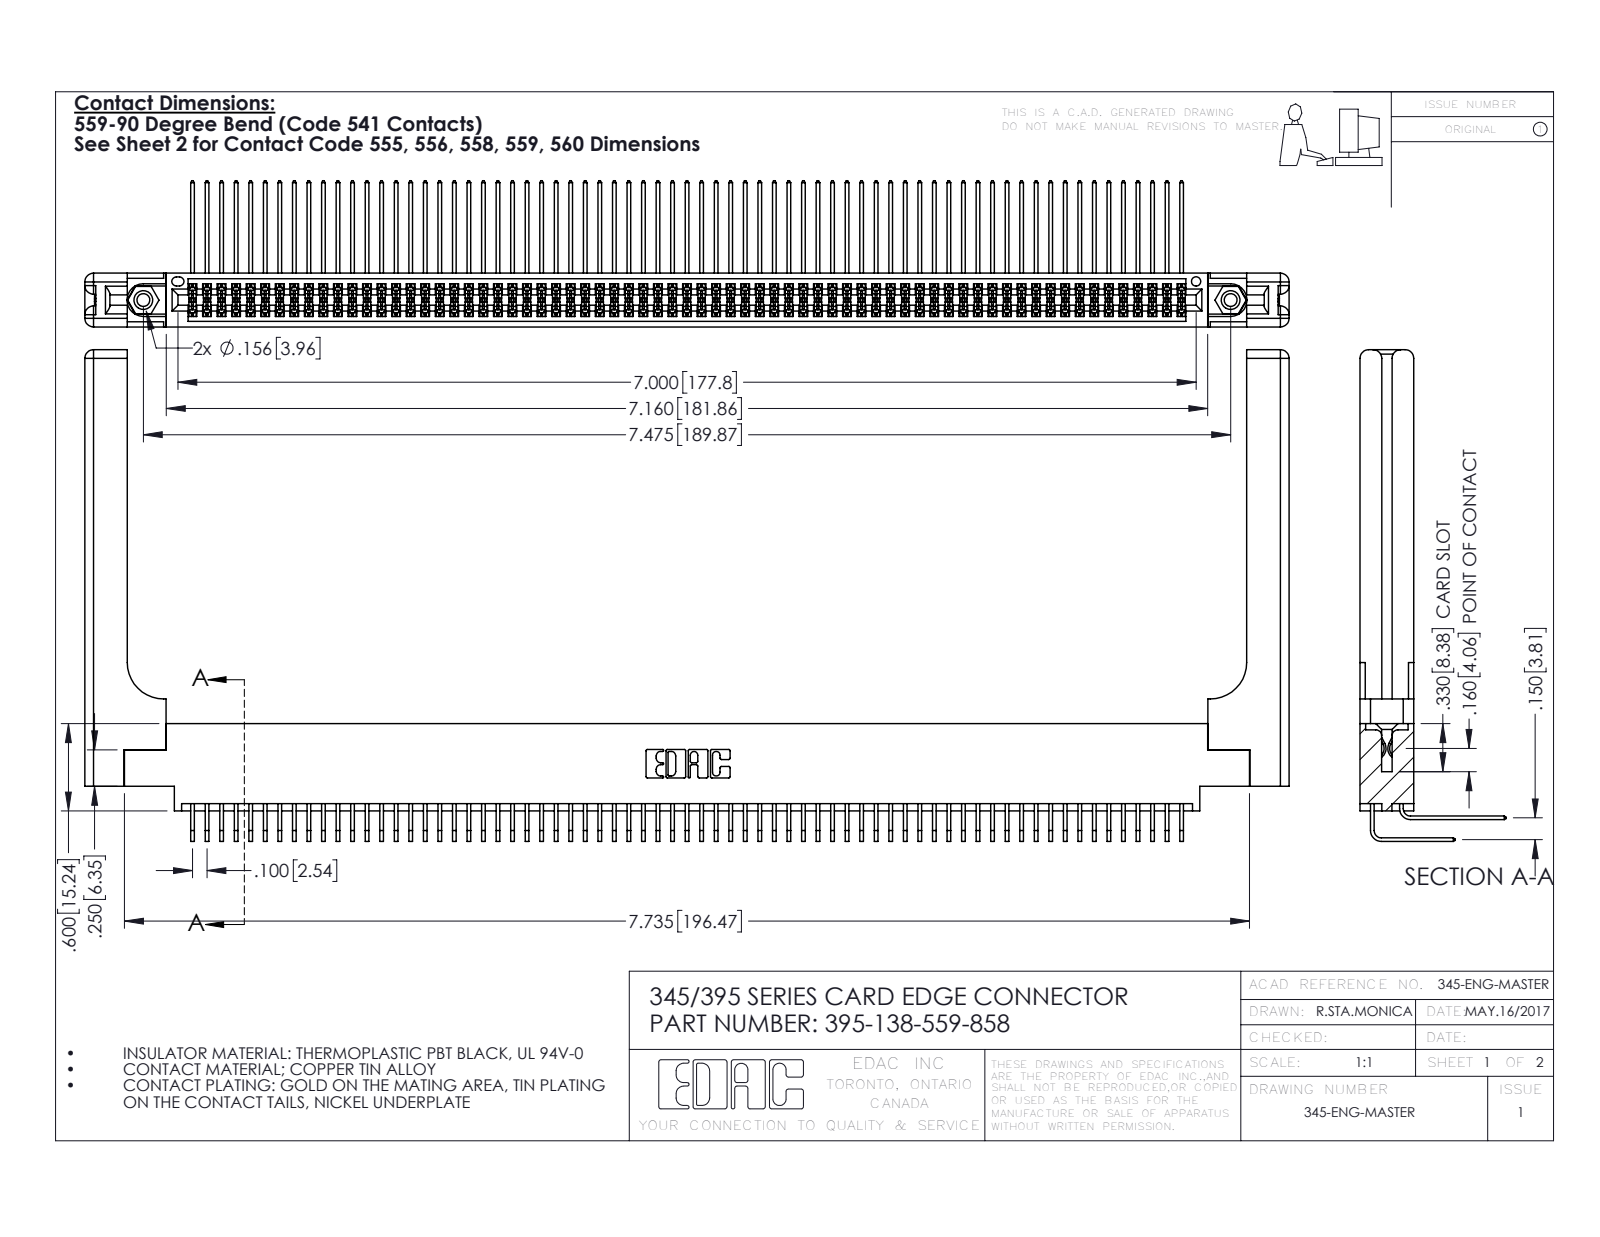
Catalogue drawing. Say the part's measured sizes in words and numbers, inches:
The part is named "345-220-058_345-220-058; 345-250-001_345-250-001-102; 345-292-001_558 559 Tail - 1; 395-138-559-858 (+2 more)". Its 3-D file was written by "SolidWorks 2016 (CONFIG_CONTROL_DESIGN)". It is 143 solids with 7562 faces: 5062 planar, 2440 cylindrical and 60 other. Overall it measures 8.279 by 3.379 by 1.005 inches. Its volume is 1.821 cubic inches and its surface area 63.62 square inches. Round holes: 2 of diameter 0.089, 2 of diameter 0.125, 2 of diameter 0.156, 1 of diameter 0.064. Round bosses or shafts: 2 of diameter 0.155. Partial cylindrical surfaces (rounded edges, fillets, slot ends): 275 of radius 0.006, 22 of radius 0.01, 16 of radius 0.06, 6 of radius 0.007, 6 of radius 0.031, 3 of radius 0.026, 2 of radius 0.014, 2 of radius 0.019. The main face-to-face distances are 0.072, 0.298, 0.37, 0.098, 0.272, 0.025, 0.2, 0.225, 0.175, 0.15. The hole center spacings are 0.27, 7.239, 7.475.
